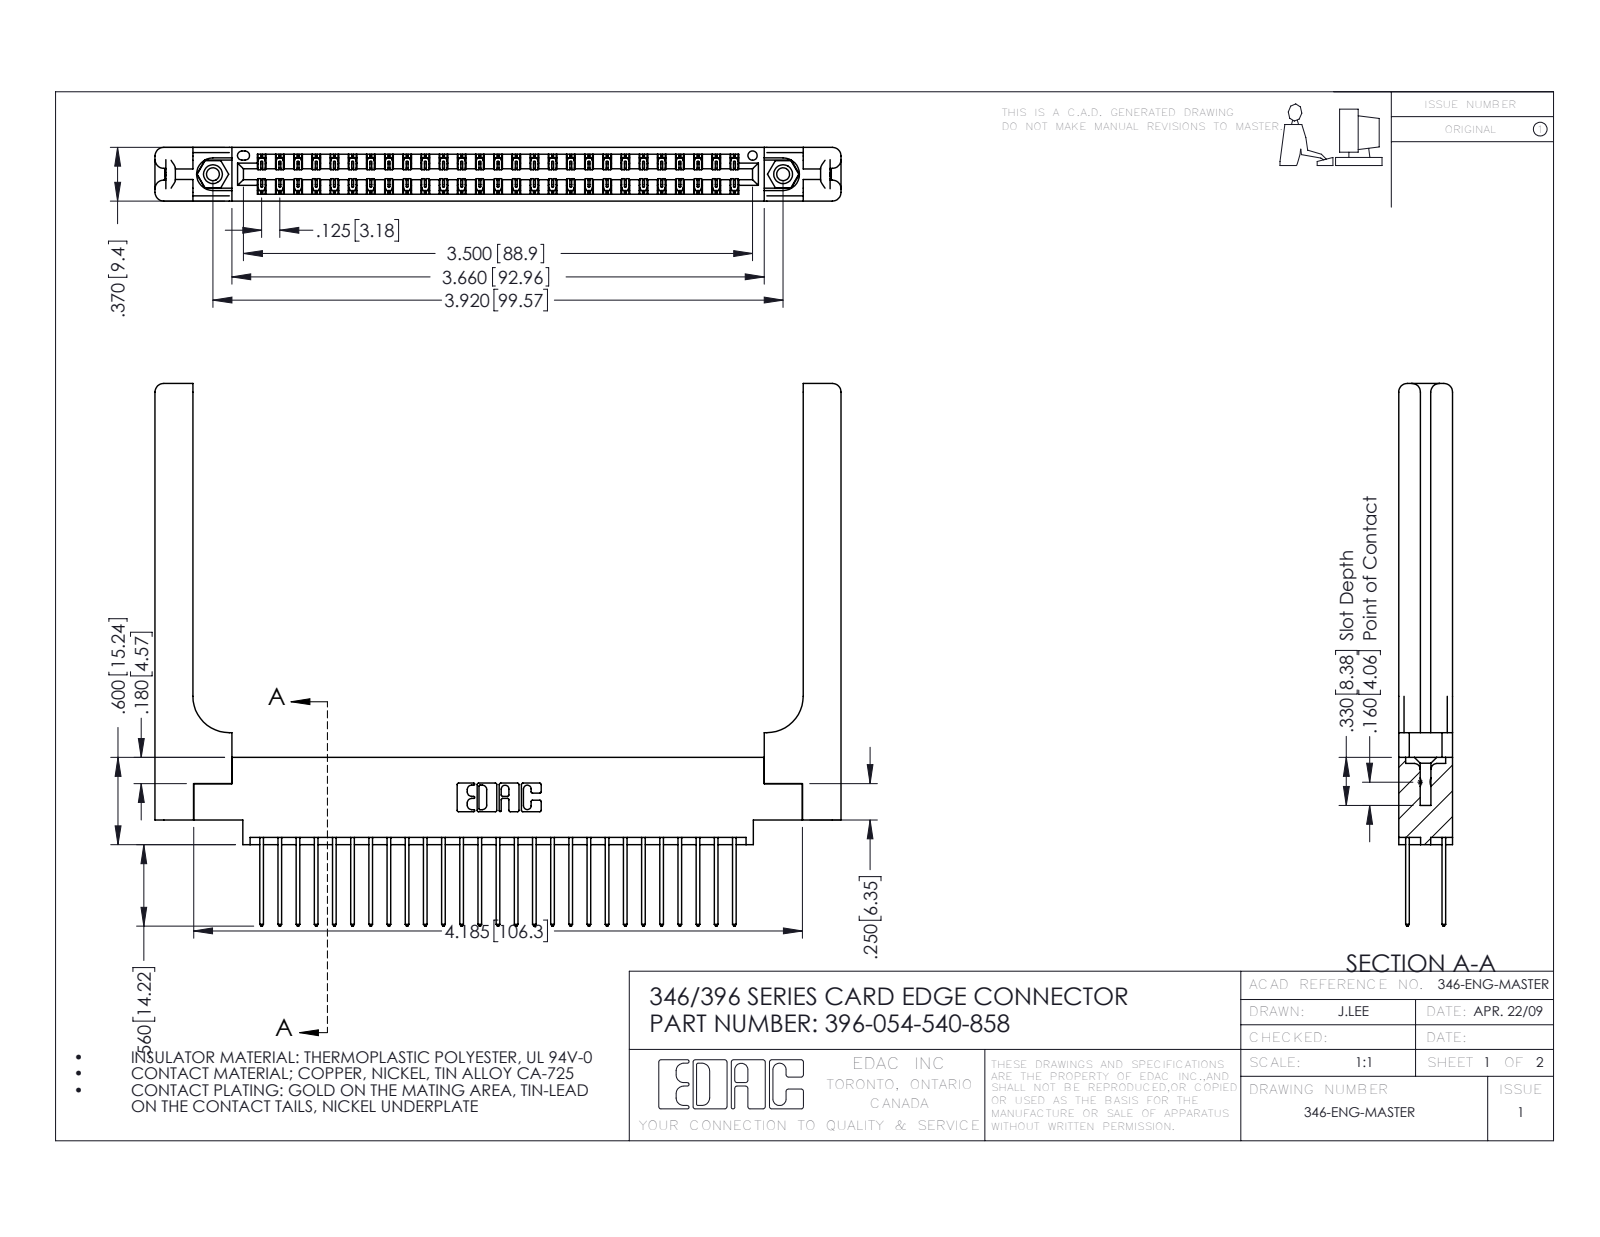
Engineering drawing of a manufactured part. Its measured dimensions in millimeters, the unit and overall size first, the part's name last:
Units: millimetres
Overall size (bounding box): 119.8 × 94.7 × 9.4
Round holes (diameter × count): ⌀2.3 ×2, ⌀3.2 ×2, ⌀4 ×2, ⌀1.6 ×1
Round bosses / shafts (diameter × count): ⌀3.9 ×2
Partial cylindrical surfaces — rounded edges, fillets, slot ends (radius × count): R0.2 ×81, R0.3 ×54, R0.3 ×22, R1.5 ×16, R0.2 ×6, R0.8 ×6, R0.7 ×3, R0.4 ×2
Main face-to-face distances: 9.4, 1.8, 1.2, 8.2, 6.4, 3.8, 3.8, 0.6, 7.6, 7
Hole centre spacings: 6.2, 94.3, 99.6
Volume: 19 110 mm³ · Surface area: 21 850 mm²
Bodies: 59 solids, 3190 faces (2118 planar, 1012 cylindrical, 60 other)
Part name (STEP PRODUCT): 396-054-540-858; 345-250-001_345-250-001-102; 346-220-058_345-220-058; 345-292-001_345-293-140 (+1 more)
STEP written by: SolidWorks 2016 (CONFIG_CONTROL_DESIGN)
